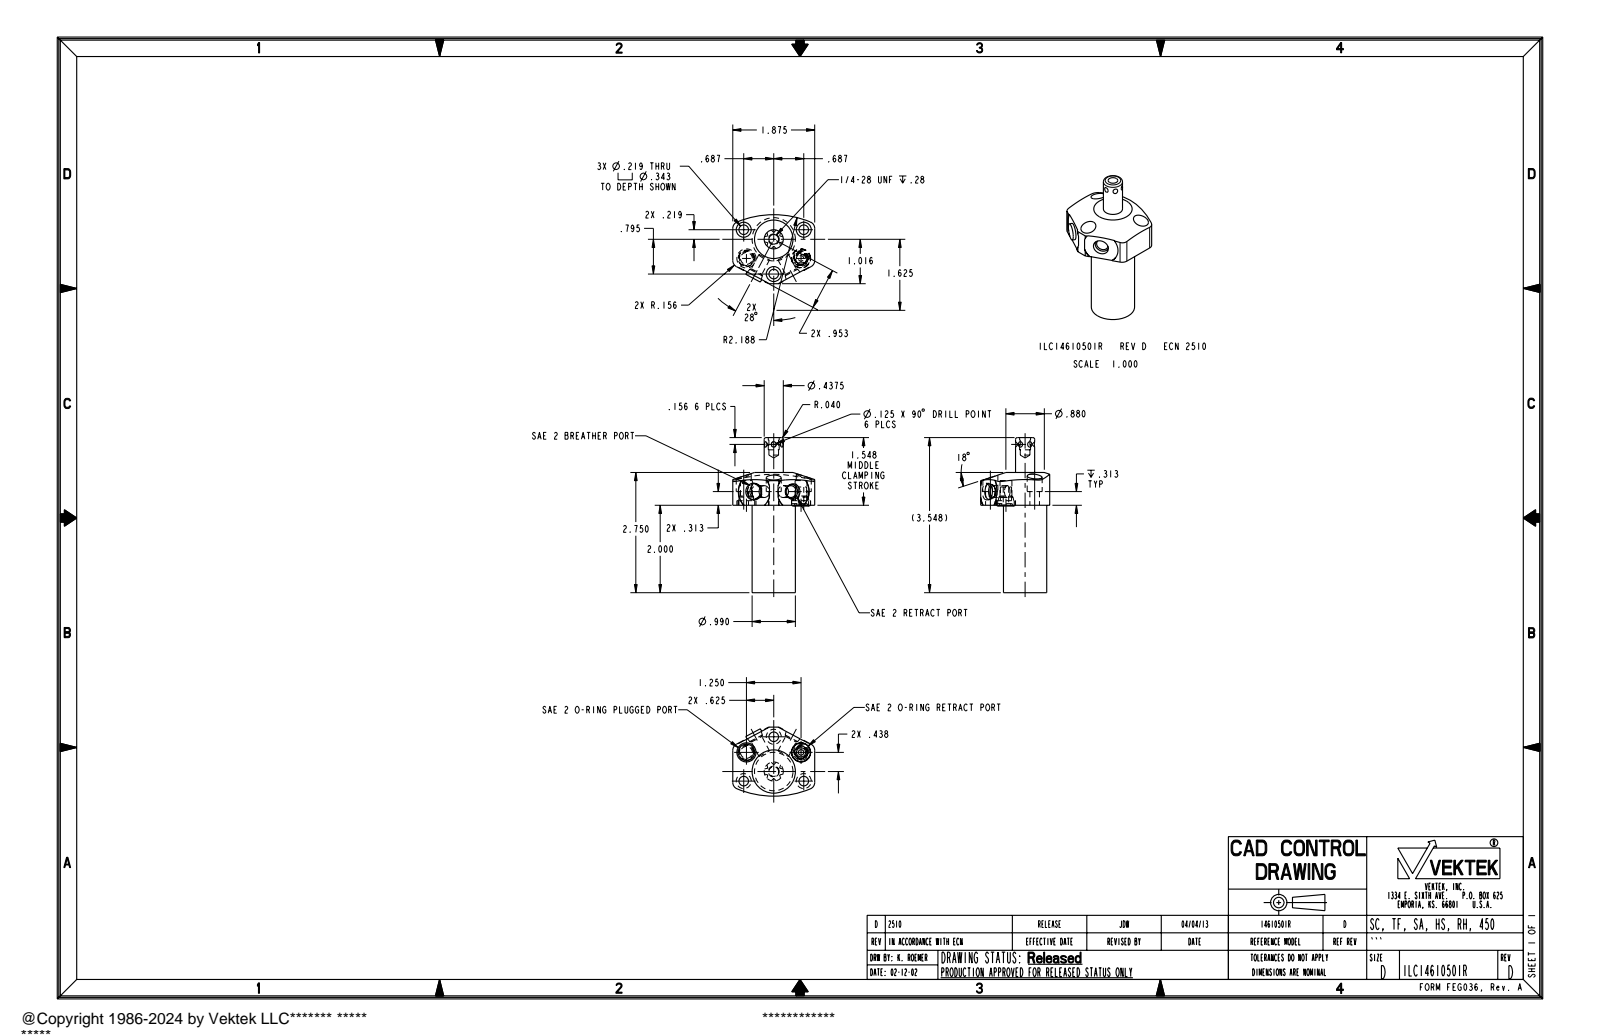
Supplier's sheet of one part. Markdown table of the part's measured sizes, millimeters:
| quantity | value |
| --- | --- |
| part name | ILC14610501R |
| STEP written by | PRO/ENGINEER BY PARAMETRIC TECHNOLOGY CORPORATION, 2007460 (AUTOMOTIVE_DESIGN_CC2) |
| units | millimeters |
| bodies | 1 solid, 127 faces (34 planar, 55 cylindrical, 38 other) |
| overall size | 90.1 × 47.6 × 40.1 |
| volume | 50 410 mm³ |
| surface area | 13 610 mm² |
| round holes (diameter × count) | 6.9 × 4, 5.6 × 3, 8.7 × 3, 11.1 × 2, 3.2 × 1, 5.6 × 1 |
| round bosses / shafts (diameter × count) | 9.6 × 2, 25.1 × 1, 11.1 × 1, 10.9 × 1, 6.5 × 1, 6.4 × 1, 5.3 × 1 |
| partial cylindrical surfaces (radius × count) | 4 × 4, 10.5 × 2, 55.6 × 1 |
| main face-to-face distances | 50.8, 69.9, 19.1, 47.6, 2.7, 8, 53.5, 16.4, 58.8, 5.3 |
| hole center spacings | 16.8, 18.3, 18.3, 19.4, 31.1, 37.3, 20.2, 31.8 |
